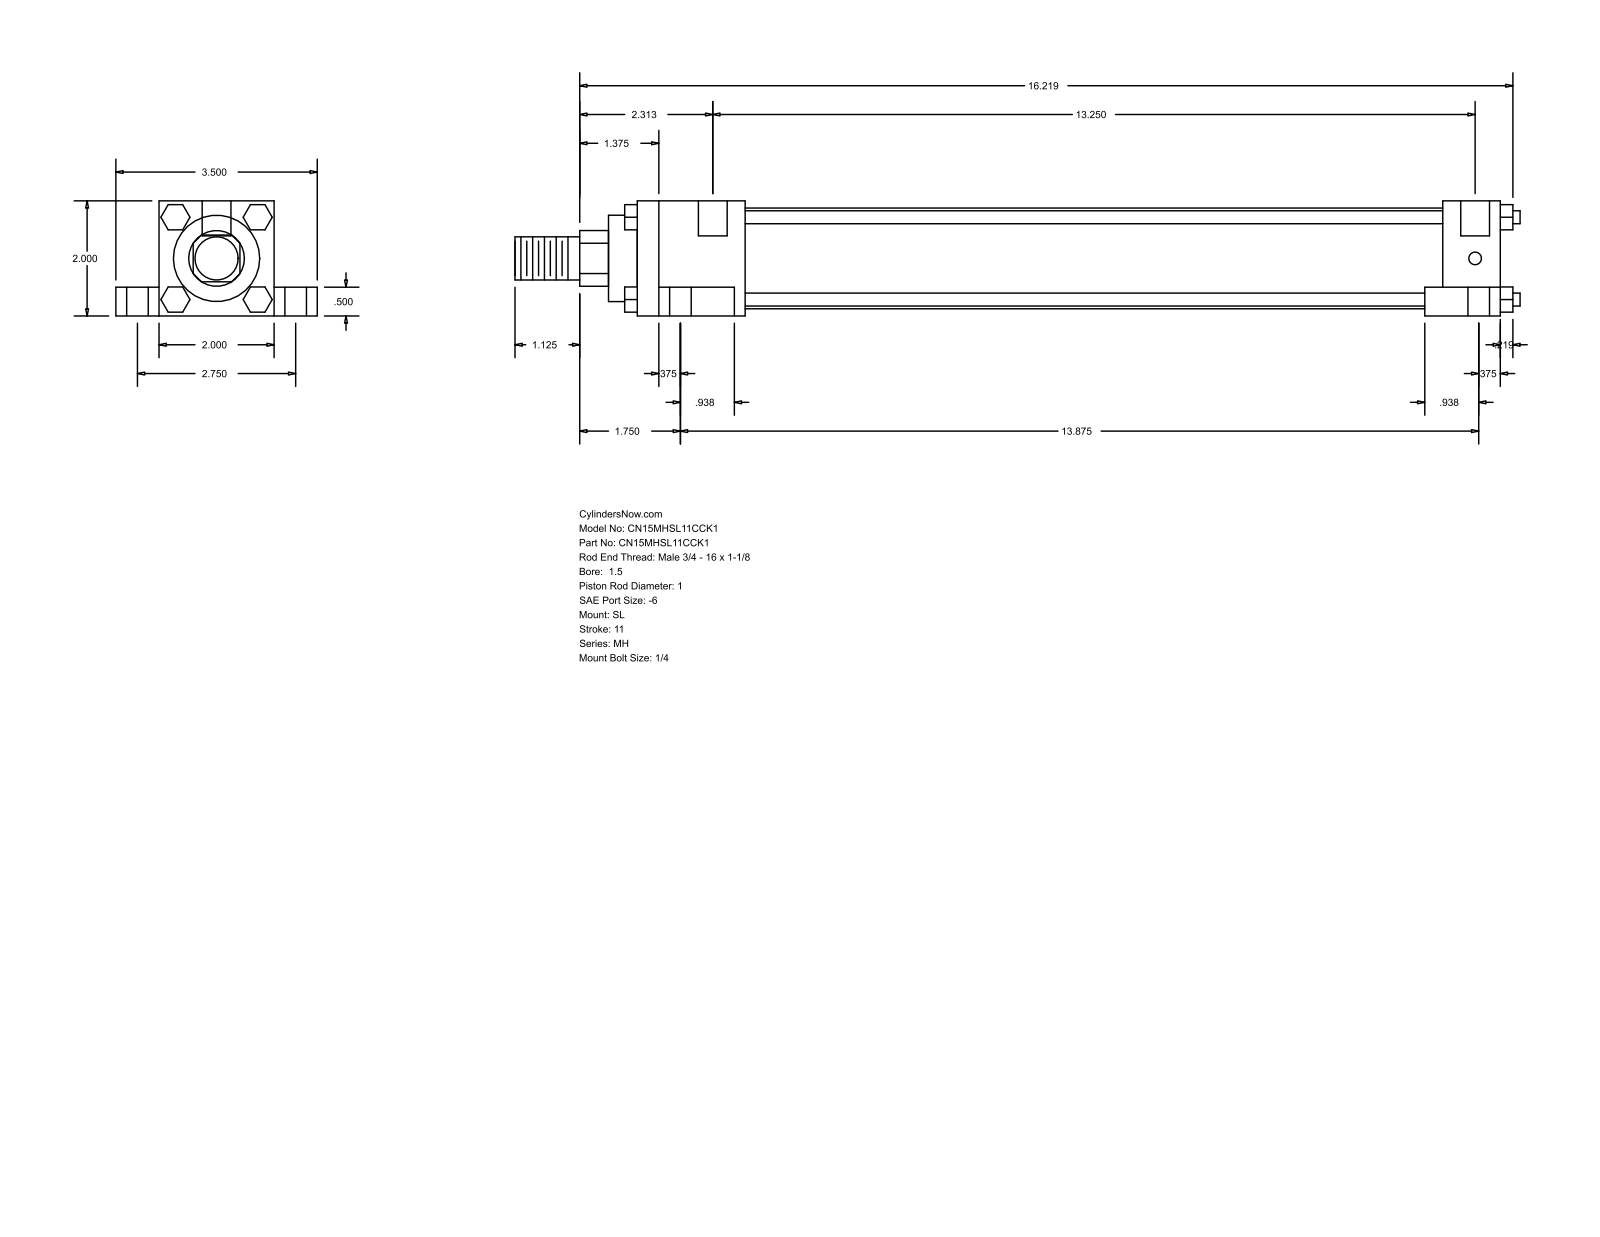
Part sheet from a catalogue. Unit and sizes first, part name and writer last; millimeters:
Units: millimetres
Overall size (bounding box): 443.71 × 88.9 × 50.8
Round holes (diameter × count): ⌀5.56 ×4, ⌀9.53 ×4, ⌀15.88 ×4, ⌀12.7 ×2
Round bosses / shafts (diameter × count): ⌀5.71 ×4, ⌀44.45 ×1, ⌀38.1 ×1, ⌀25.4 ×1, ⌀19.05 ×1
Partial cylindrical surfaces — rounded edges, fillets, slot ends (radius × count): R12.29 ×1
Main face-to-face distances: 50.8, 12.7, 38.1, 19.05, 69.85, 381, 25.4, 9.52, 33.34, 338.14
Hole centre spacings: 34.96, 36.64, 37.73, 69.84, 339.73, 339.94, 343.1, 352.43
Bodies: 0 solids, 148 faces (112 planar, 36 cylindrical, 0 other)
Part name (STEP PRODUCT): MH_SL__0150_1
STEP written by: GSSL Pune (CONFIG_CONTROL_DESIGN)
